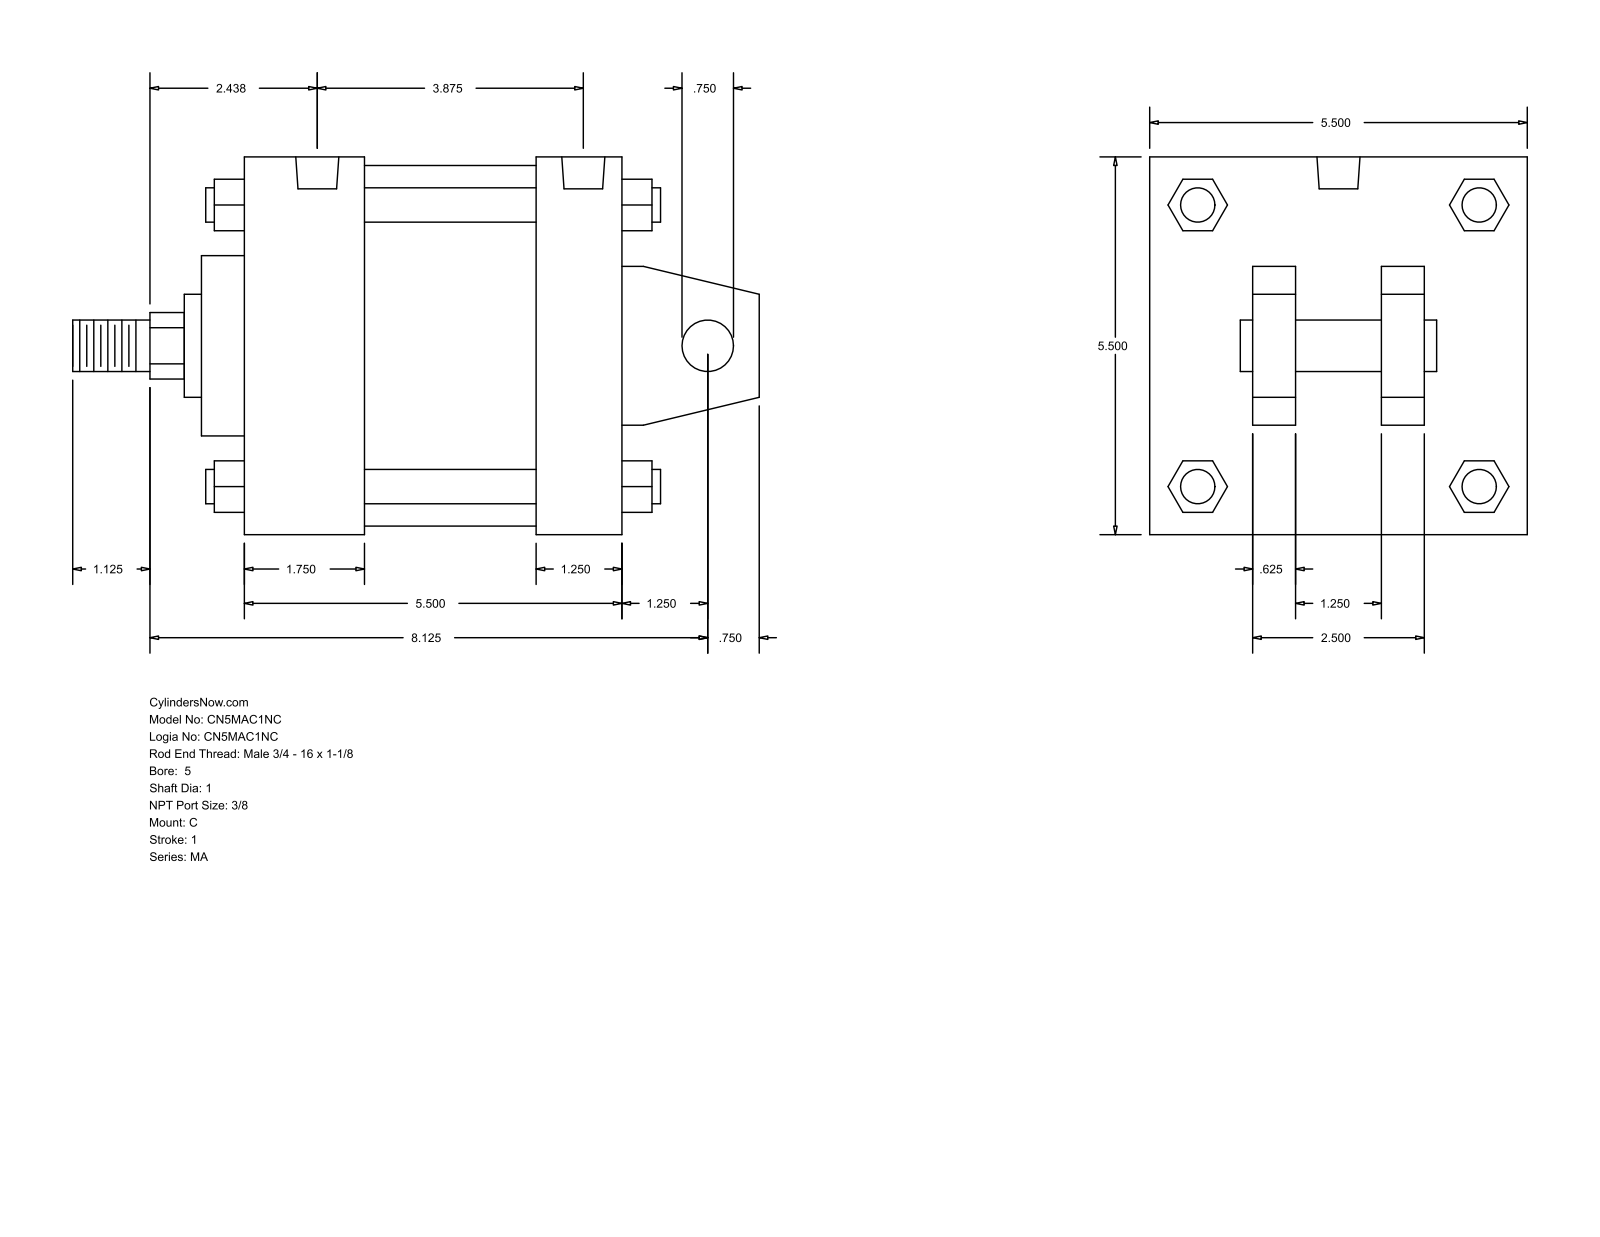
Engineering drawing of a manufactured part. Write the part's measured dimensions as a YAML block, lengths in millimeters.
part_name: "MA_C__0500_1"
step_written_by: "GSSL Pune (CONFIG_CONTROL_DESIGN)"
units: millimeters
bodies: {solids: 0, faces: 141, planar: 109, cylindrical: 32, other: 0}
overall_size: [254, 139.7, 139.7]
round_holes:
  - {diameter: 11.11, count: 4}
  - {diameter: 15.93, count: 2}
round_bosses_or_shafts:
  - {diameter: 12.7, count: 4}
  - {diameter: 19.05, count: 2}
  - {diameter: 133.35, count: 1}
  - {diameter: 66.67, count: 1}
  - {diameter: 38.1, count: 1}
  - {diameter: 25.4, count: 1}
partial_cylinders:
  - {radius: 12.29, count: 1}
face_to_face_distances: [139.7, 63.5, 15.87, 107.96, 31.74, 44.46, 95.24, 38.1, 101.6, 53.97]
hole_center_spacings: [88.9, 4.76, 4.77, 93.66, 93.67, 98.43]
